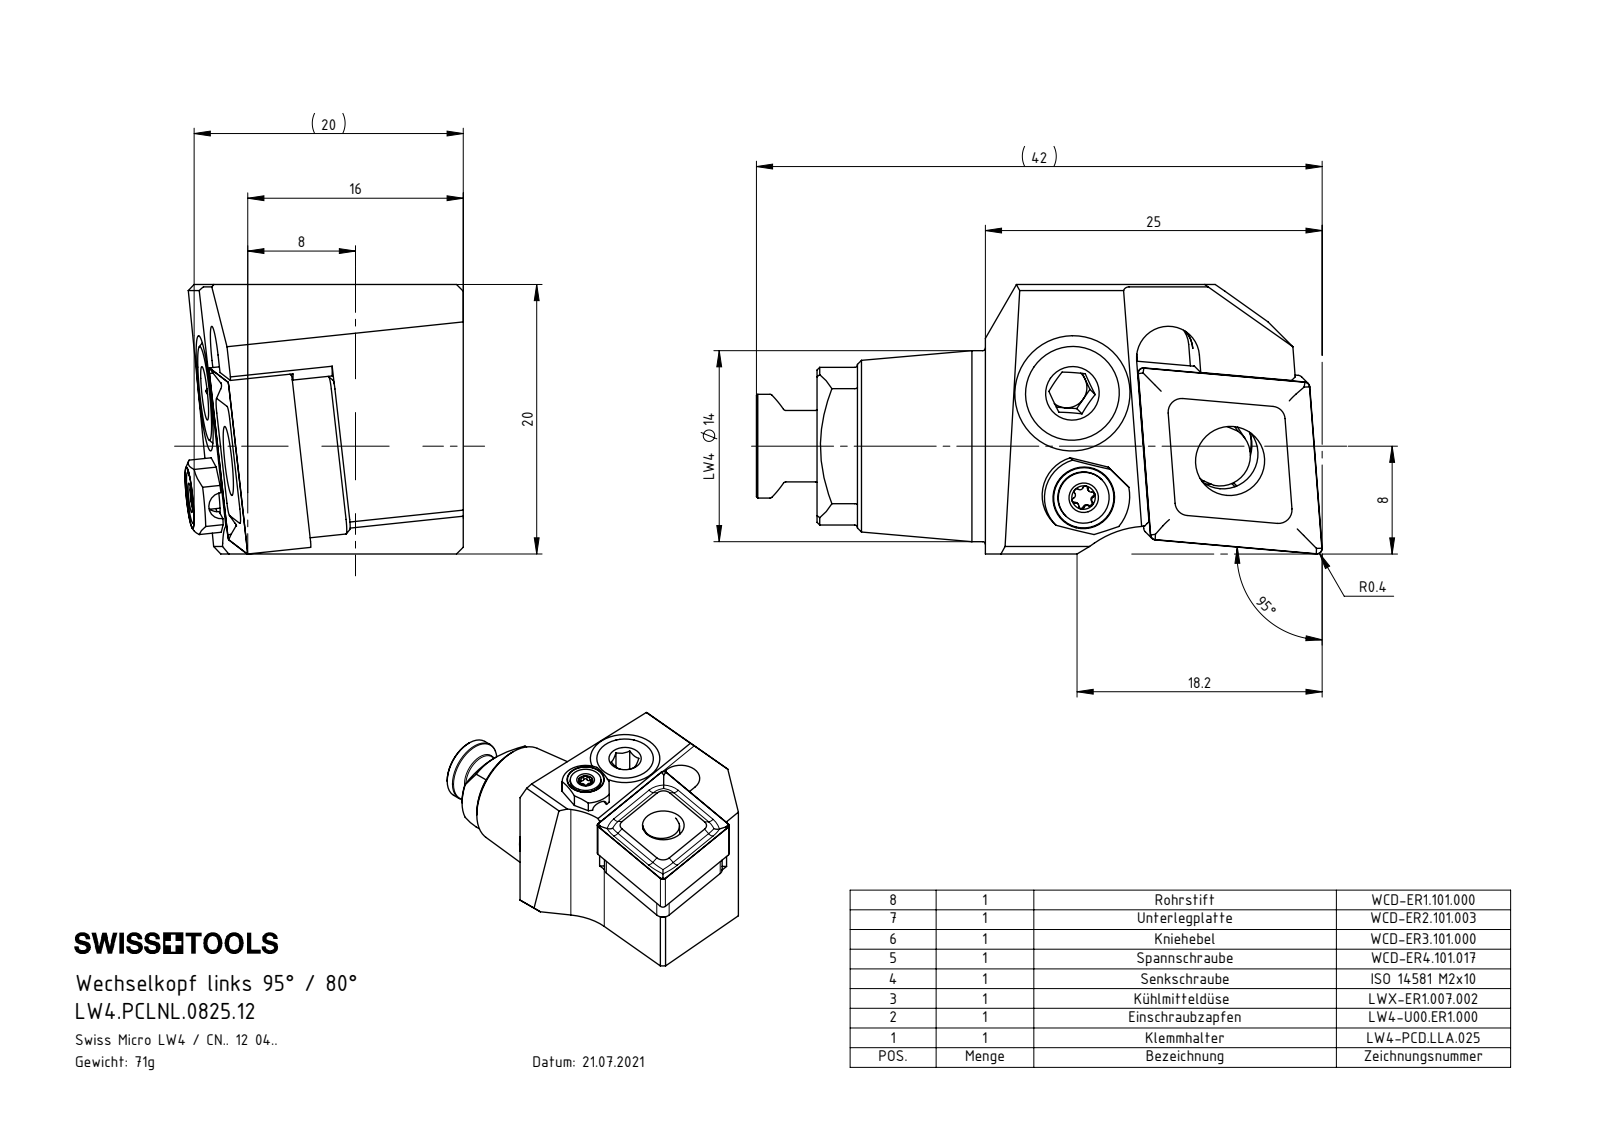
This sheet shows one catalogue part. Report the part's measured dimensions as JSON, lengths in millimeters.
{"part_name": "WCD-ER2.101.003_A; LW4-PCD.LLA.025_A; ISO 14581 - M2x10; CNMG120404 (+4 more)", "step_written_by": "SolidWorks 2022 (CONFIG_CONTROL_DESIGN)", "units": "millimeters", "bodies": {"solids": 7, "faces": 280, "planar": 101, "cylindrical": 83, "other": 96}, "overall_size": [37.5, 20.55, 20], "volume_mm3": 7836, "surface_area_mm2": 5782, "round_holes": [[3, 2], [1.6, 1], [2, 1], [5.16, 1], [5.5, 1], [6.55, 1], [7, 1], [8.4, 1]], "round_bosses_or_shafts": [[14.17, 1], [8, 1], [7.9, 1], [6.4, 1], [4.5, 1], [3.8, 1], [3.55, 1], [2, 1]], "partial_cylinders_radius": [[0.2, 8], [0.24, 6], [0.4, 4], [1, 4], [2.5, 2], [0.5, 1], [2.1, 1], [2.2, 1]], "face_to_face_distances": [11.7, 4.76, 3.18, 7.94, 1, 12.7, 4.71, 0.5, 11.2, 12.2], "hole_center_spacings": [7.62, 11.39, 11.43, 12.86, 12.93]}
